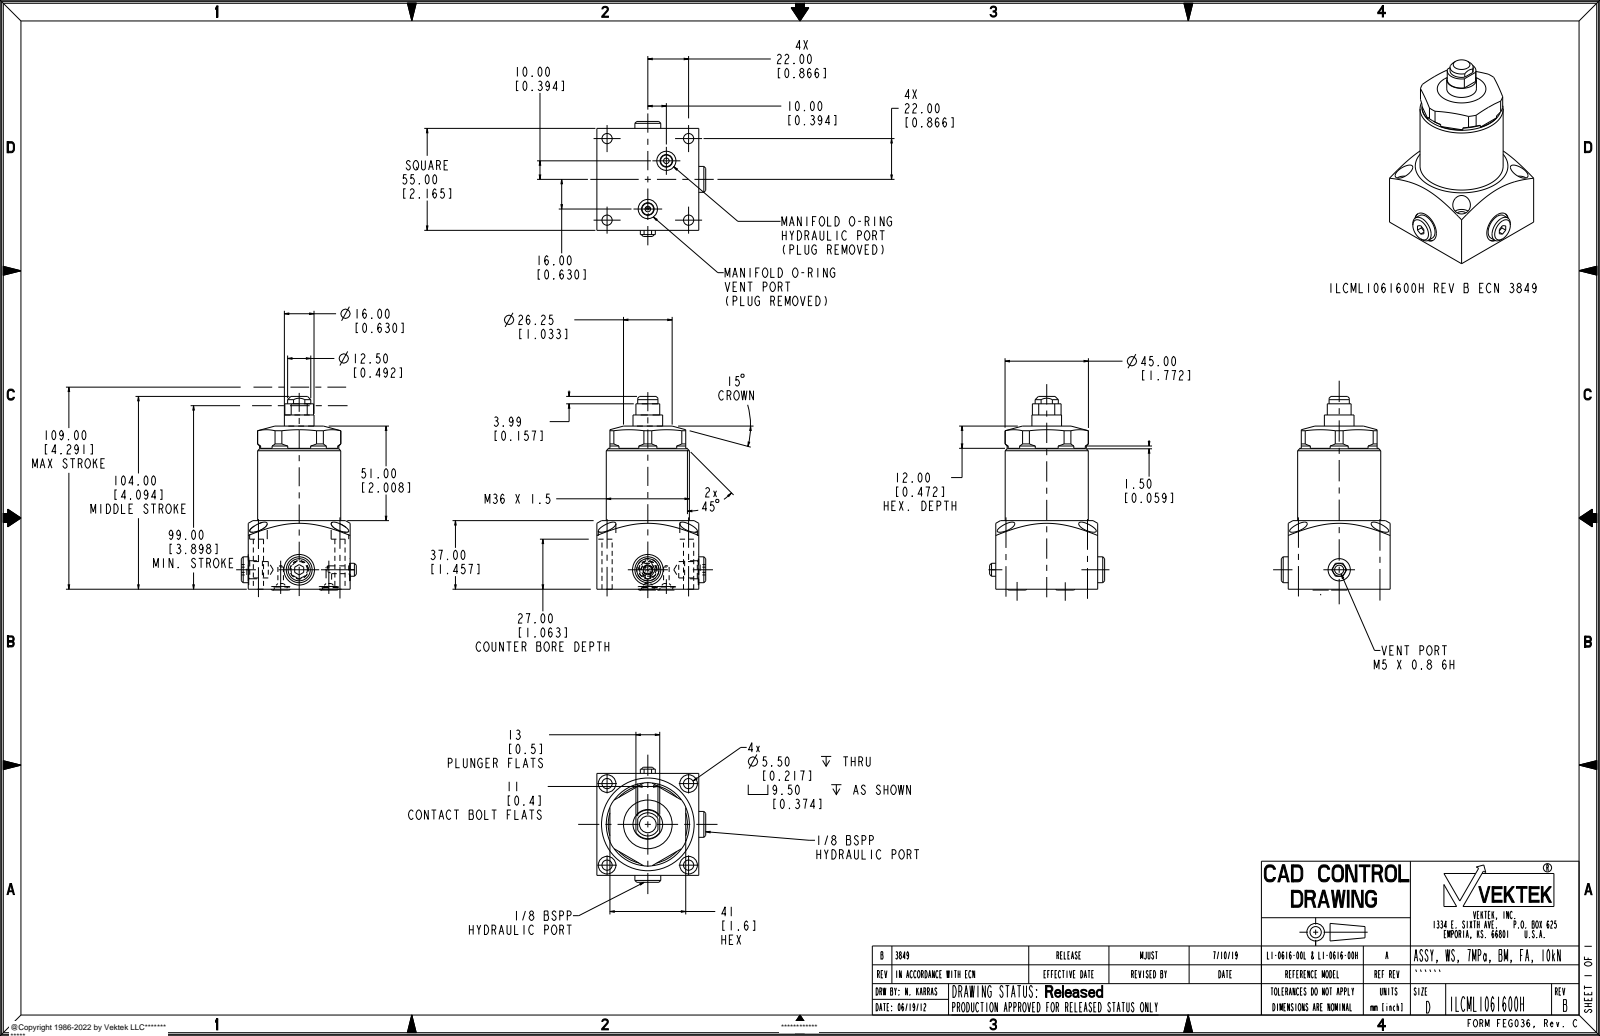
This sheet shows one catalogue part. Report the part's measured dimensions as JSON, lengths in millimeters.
{"part_name": "ILCML1061600H", "step_written_by": "PRO/ENGINEER BY PARAMETRIC TECHNOLOGY CORPORATION, 2017170 (AUTOMOTIVE_DESIGN)", "units": "millimeters", "bodies": {"solids": 1, "faces": 181, "planar": 69, "cylindrical": 64, "other": 48}, "overall_size": [104.45, 62.07, 58.75], "volume_mm3": 184464, "surface_area_mm2": 25956, "round_holes": [[5.5, 4], [9.5, 4], [3, 2], [8.84, 2], [16.51, 2], [4.2, 1], [10, 1], [10.39, 1], [12, 1]], "round_bosses_or_shafts": [[13.97, 2], [9.73, 2], [44.85, 1], [42.75, 1], [16, 1]], "partial_cylinders_radius": [[6.25, 1], [7.75, 1], [22.5, 1]], "face_to_face_distances": [55, 40.92, 37, 54.75, 7.04, 47.96, 88, 51, 27, 10], "hole_center_spacings": [44, 22.8, 34.18, 43.91, 62.23, 16.97, 27.86, 45.25]}
